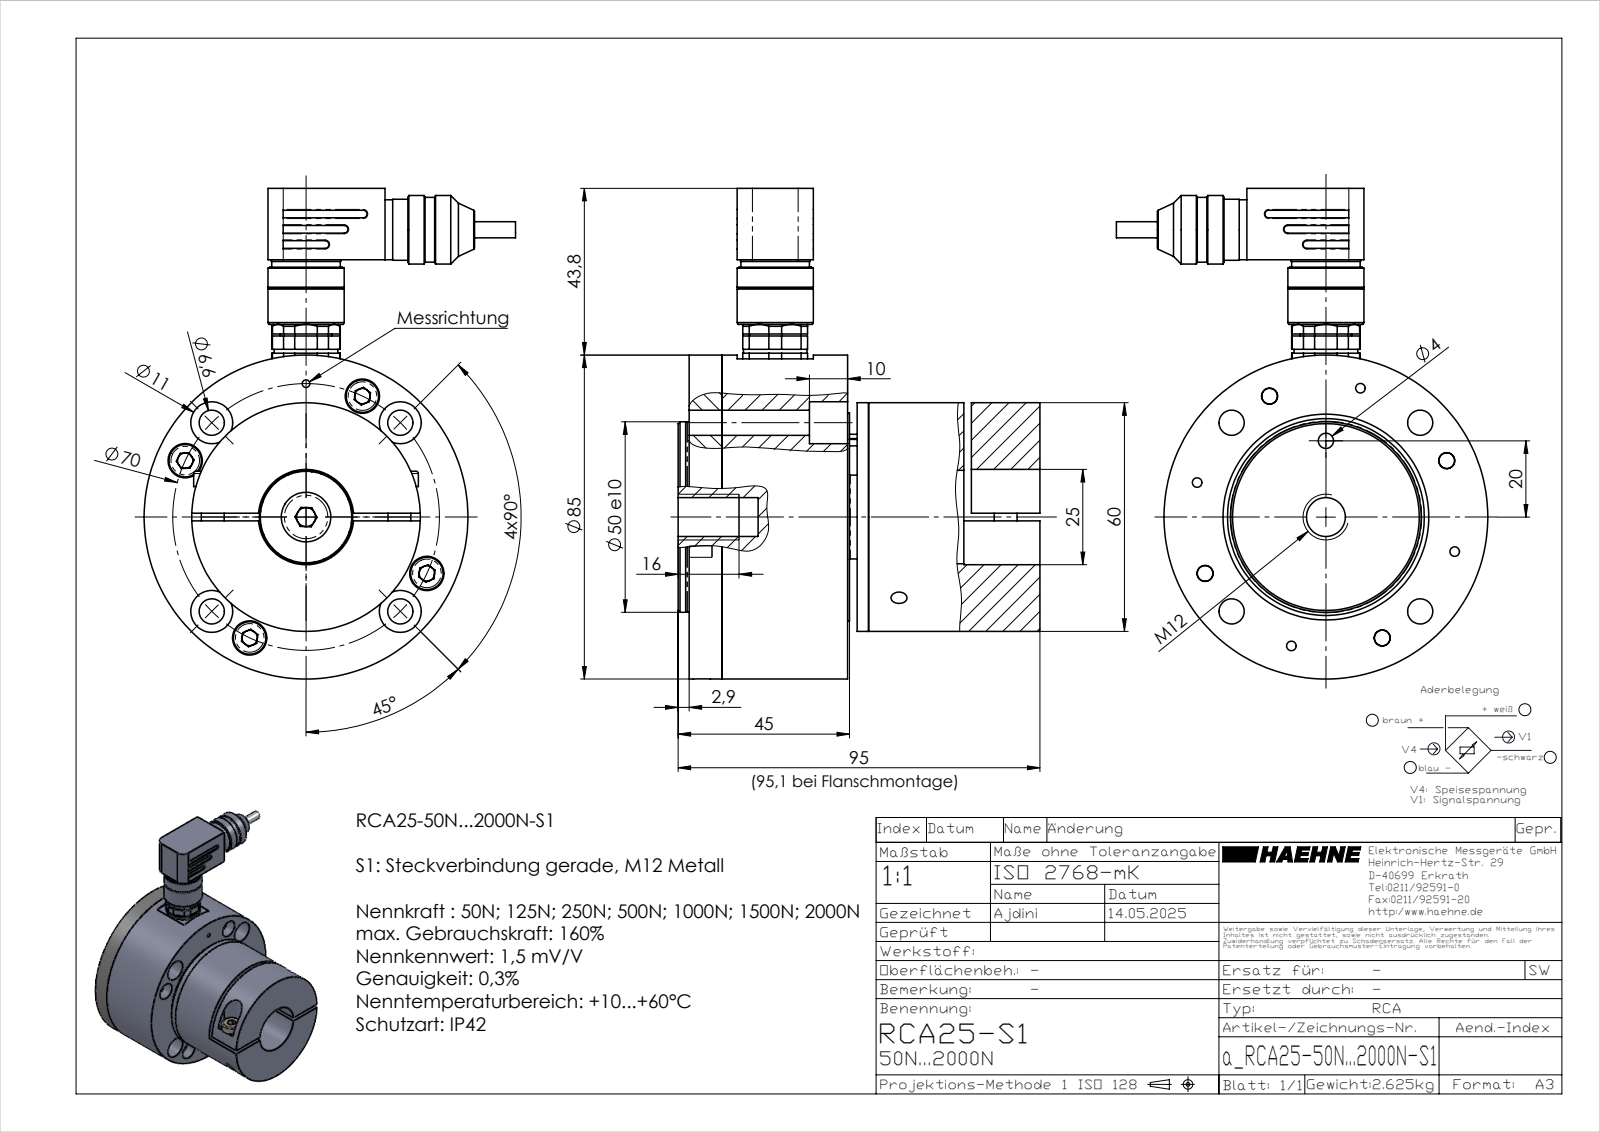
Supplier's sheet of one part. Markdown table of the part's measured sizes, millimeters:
| quantity | value |
| --- | --- |
| part name | inafag_1203-tvh_7zkvytp7yxkimpdvw8sj0b5w4_16; inafag_1203-tvh_7zkvytp7yxkimpdvw8sj0b5w4_03; Y02043Z1 inafag_1203-tvh_7zkvytp7yxkimpdvw8sj0b5w4; inafag_1203-tvh_7zkvytp7yxkimpdvw8sj0b5w4_04 (+8 more) |
| STEP written by | SolidWorks 2023 (AUTOMOTIVE_DESIGN) |
| units | millimeters |
| bodies | 55 solids, 808 faces (408 planar, 228 cylindrical, 172 other) |
| overall size | 128.75 × 97.48 × 95.1 |
| volume | 380 770 mm³ |
| surface area | 116 479 mm² |
| round holes (diameter × count) | 3.4 × 9, 2.5 × 8, 6.6 × 6, 4.2 × 5, 4 × 4, 5.3 × 4, 9 × 4, 11 × 4, 4.5 × 2, 5 × 2, 2 × 1, 6 × 1 |
| round bosses / shafts (diameter × count) | 3 × 9, 5.7 × 8, 8.5 × 4, 5 × 4, 1.5 × 4, 1 × 4, 18 × 2, 17 × 2 |
| partial cylindrical surfaces (radius × count) | 0.2 × 12, 1 × 11, 0.3 × 6, 4 × 2, 5.5 × 2, 0.57 × 1, 0.65 × 1, 0.77 × 1 |
| main face-to-face distances | 2, 3, 8.6, 47.1, 35.5, 45, 11.6, 50, 30, 50.1 |
| hole center spacings | 35, 49.5, 24.78, 25.2, 32.8, 51.14, 56.46, 6 |
